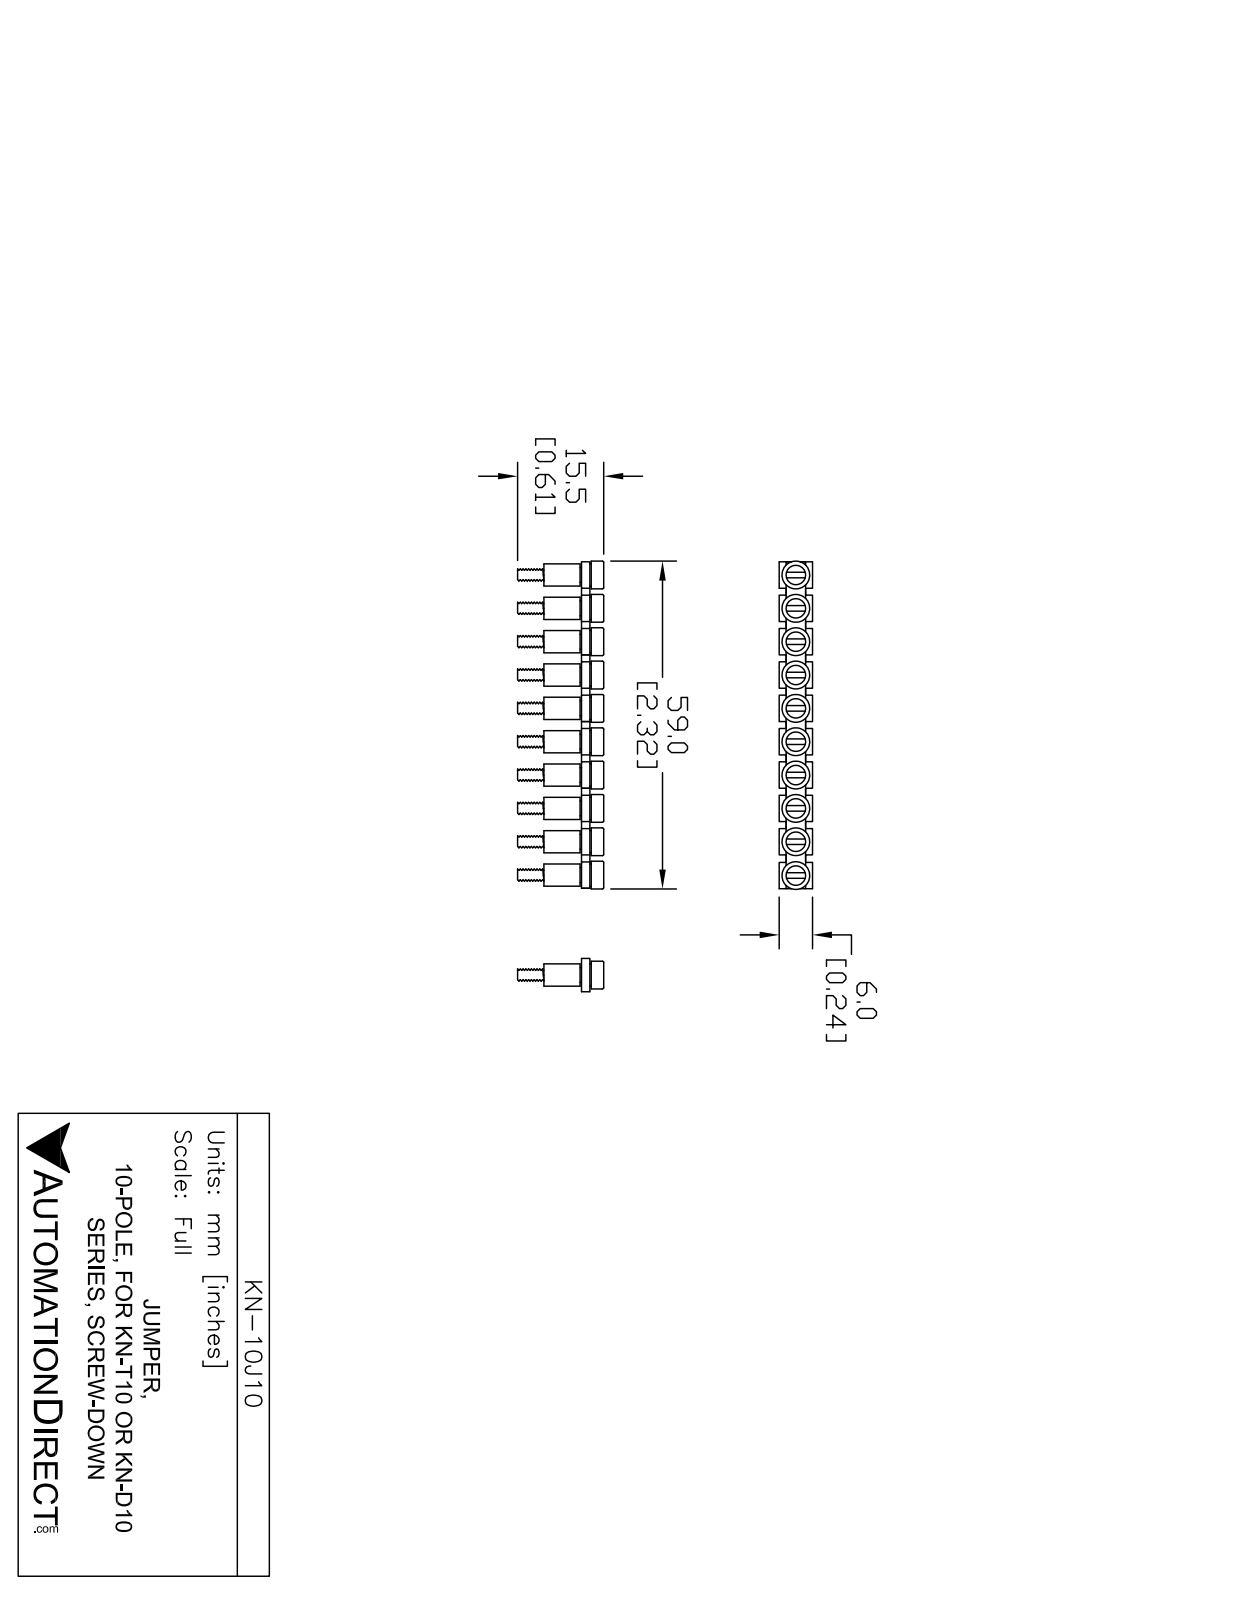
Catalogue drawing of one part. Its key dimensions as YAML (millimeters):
part_name: "KN-10J10"
step_written_by: "SolidWorks 2014 (AUTOMOTIVE_DESIGN)"
units: millimeters
bodies: {solids: 31, faces: 418, planar: 208, cylindrical: 150, other: 60}
overall_size: [59, 15.5, 6]
volume: 1826
surface_area: 4966
round_holes:
  - {diameter: 3, count: 10}
  - {diameter: 3.15, count: 10}
  - {diameter: 3.5, count: 10}
round_bosses_or_shafts:
  - {diameter: 5, count: 10}
  - {diameter: 4, count: 10}
  - {diameter: 2.65, count: 10}
face_to_face_distances: [1.5, 1.75, 2, 6, 1, 3.5, 2.5, 4.75, 13, 4]
hole_center_spacings: [6, 12, 18, 24, 30, 36, 42, 48]
